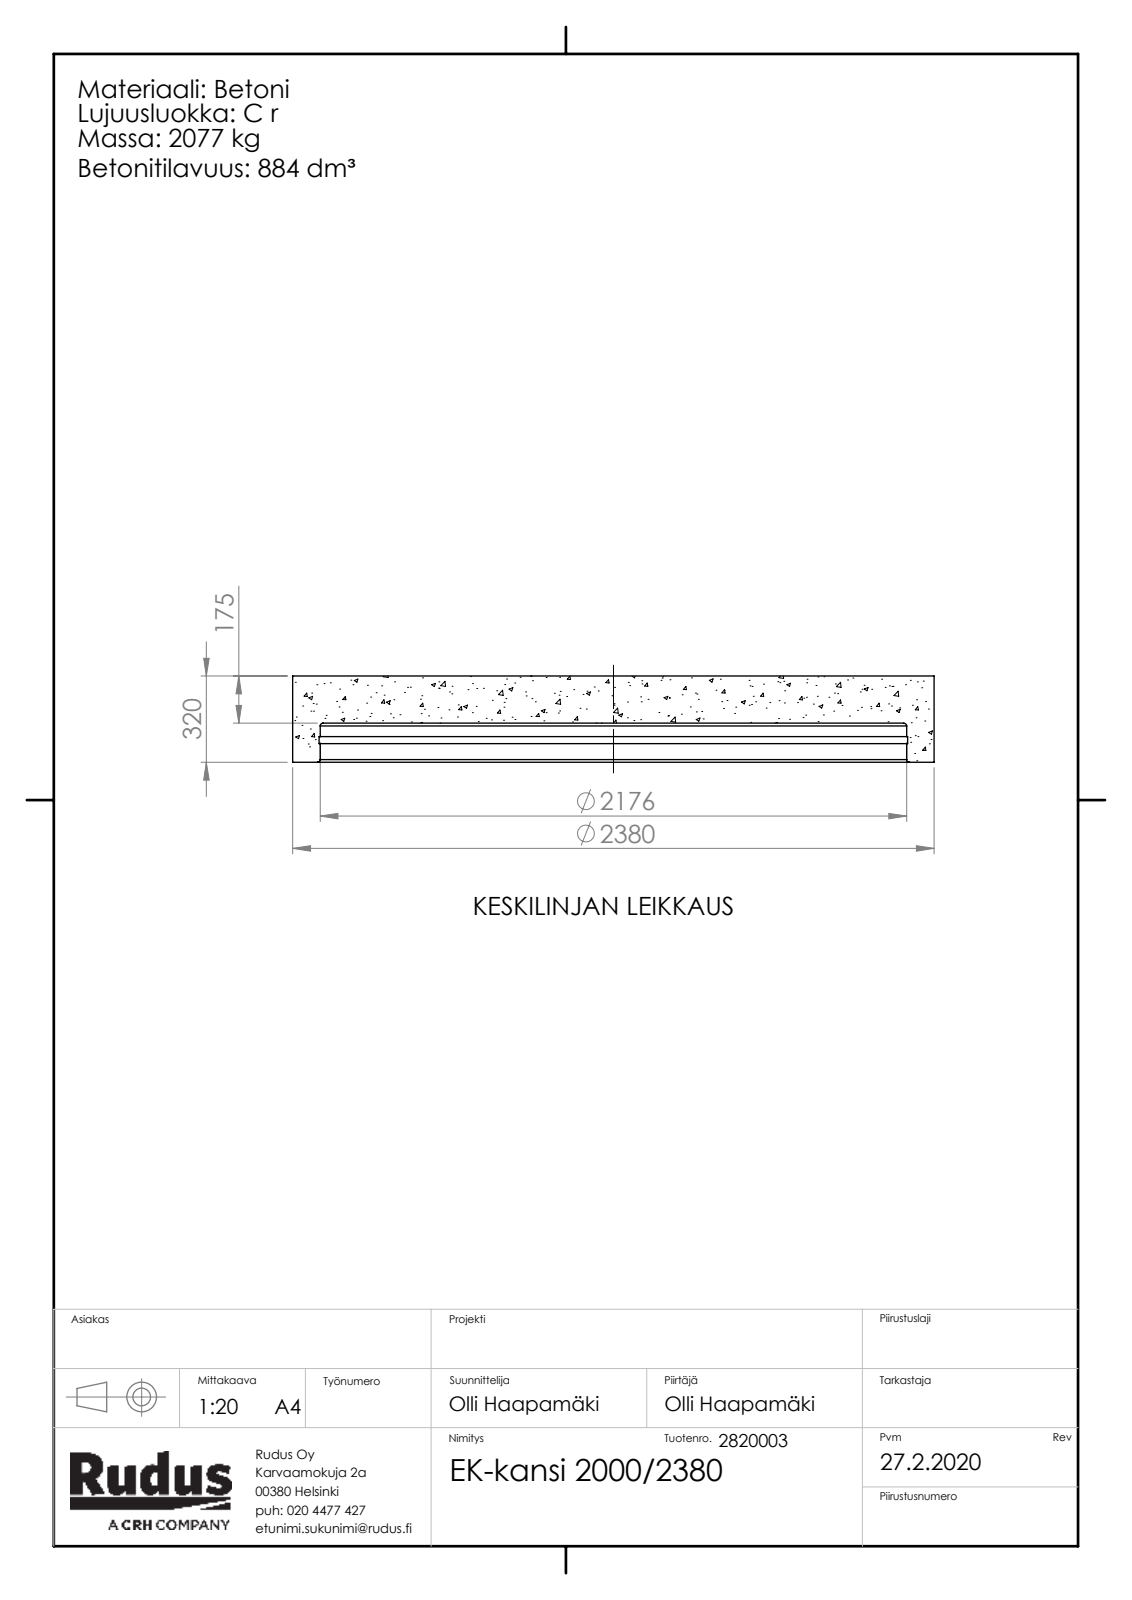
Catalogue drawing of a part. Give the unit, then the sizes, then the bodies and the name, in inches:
Units: inches
Overall size (bounding box): 93.701 × 93.701 × 12.598
Round holes (diameter × count): ⌀85.669 ×1, ⌀85.984 ×1
Round bosses / shafts (diameter × count): ⌀93.701 ×1
Partial cylindrical surfaces — rounded edges, fillets, slot ends (radius × count): R46.732 ×1
Main face-to-face distances: 6.89, 5.709, 12.598, 2.717, 2.992, 9.882, 3.74, 1.024, 1.969, 8.858
Volume: 53 920 in³ · Surface area: 19 030 in²
Bodies: 1 solid, 94 faces (13 planar, 15 cylindrical, 66 other)
Part name (STEP PRODUCT): Rudus 2820003 EK-kansi 2000_2380; EK-osa-kansi_Umpi
STEP written by: SolidWorks 2019 (CONFIG_CONTROL_DESIGN)
